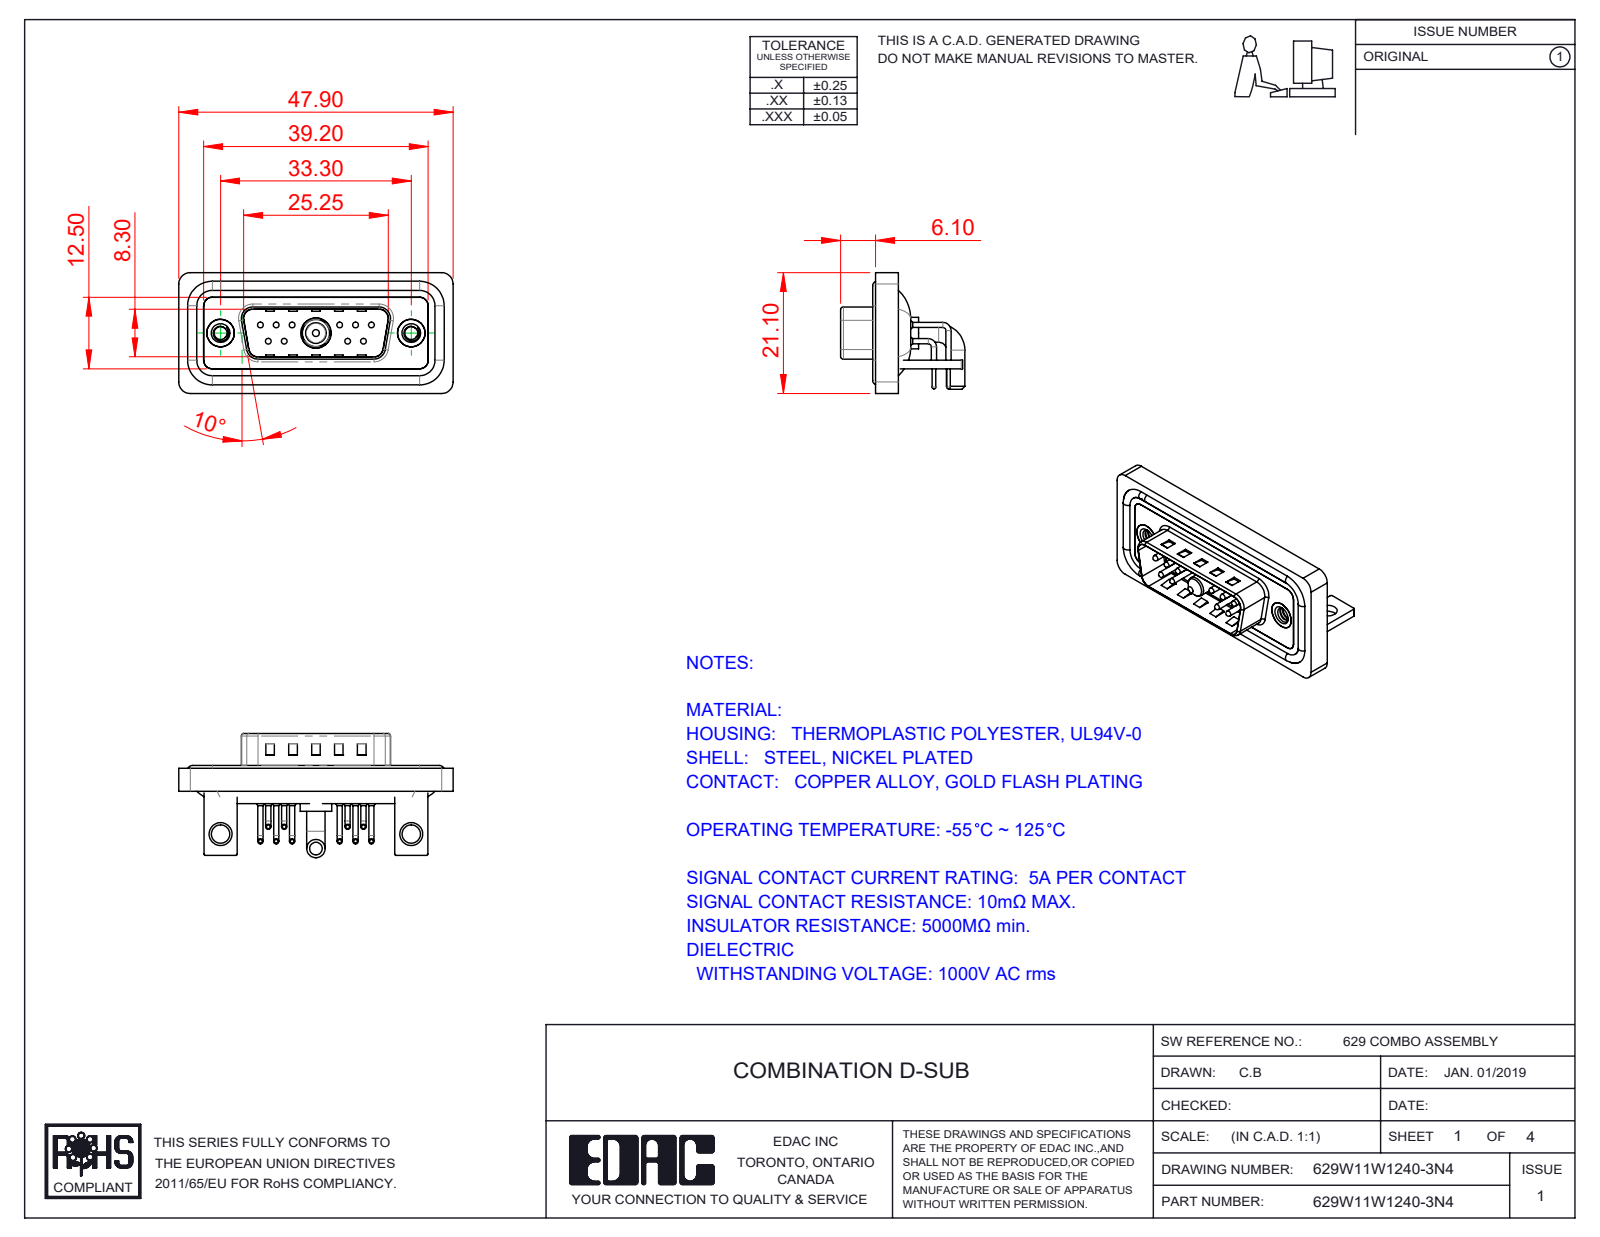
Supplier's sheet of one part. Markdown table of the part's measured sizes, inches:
| quantity | value |
| --- | --- |
| part name | 629Combo Shell Rear_15 Contacts; 629W11W1240-3N4; 629Combo Housing_11W1; 629Combo Stabilizer Bracket (+6 more) |
| STEP written by | SolidWorks 2020 (CONFIG_CONTROL_DESIGN) |
| units | inches |
| bodies | 21 solids, 1643 faces (856 planar, 587 cylindrical, 200 other) |
| overall size | 1.886 × 0.854 × 0.831 |
| volume | 0.36 in³ |
| surface area | 15.32 in² |
| round holes (diameter × count) | 0.03 × 10, 0.063 × 10, 0.079 × 10, 0.089 × 2, 0.126 × 2, 0.157 × 2, 0.189 × 2, 0.197 × 2, 0.191 × 1, 0.209 × 1 |
| round bosses / shafts (diameter × count) | 0.035 × 20, 0.059 × 10, 0.039 × 10, 0.026 × 10, 0.063 × 4, 0.193 × 2, 0.126 × 2, 0.217 × 1 |
| partial cylindrical surfaces (radius × count) | 0.079 × 21, 0.059 × 18, 0.01 × 16, 0.04 × 10, 0.02 × 9, 0.063 × 8, 0.039 × 7, 0.024 × 4 |
| main face-to-face distances | 0.016, 0.031, 0.059, 0.114, 0.083, 0.043, 0.063, 0.047, 0.146, 0.161 |
| hole center spacings | 0.124, 0.109, 0.545, 0.436, 0.654, 0.198, 0.198, 0.218 |
